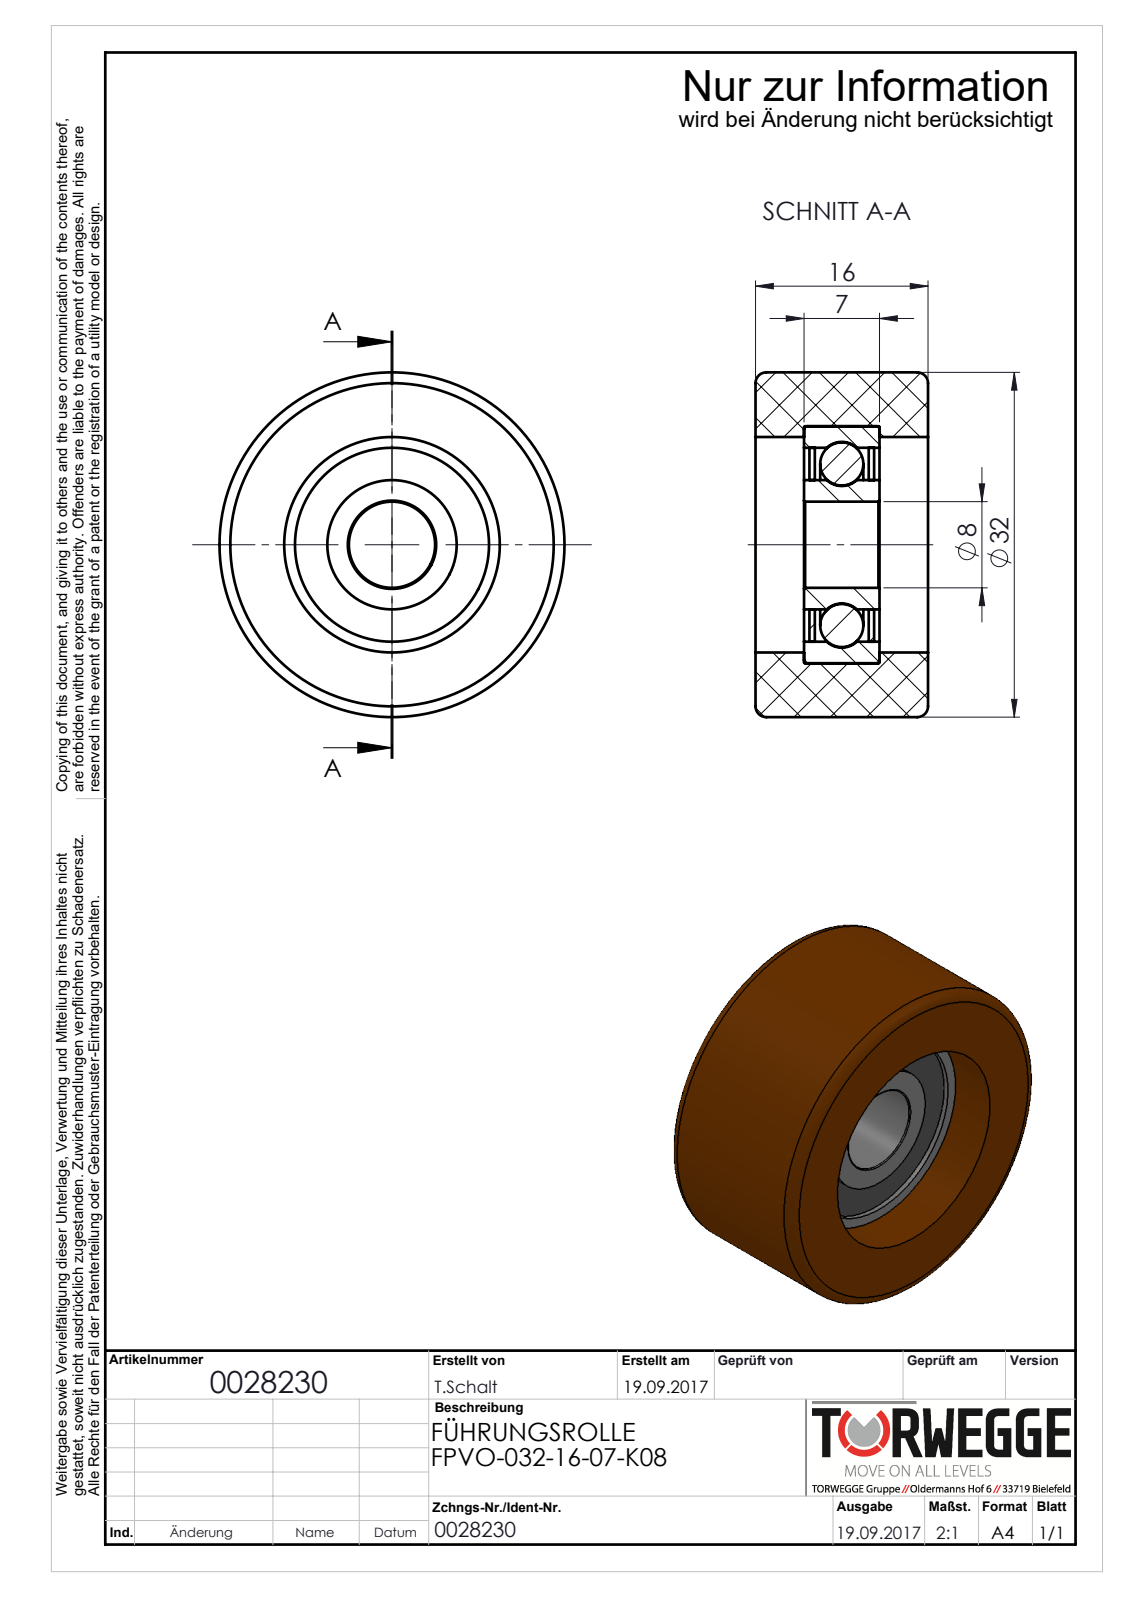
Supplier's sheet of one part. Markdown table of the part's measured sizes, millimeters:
| quantity | value |
| --- | --- |
| part name | FPVO-032-16-07-K08_Bandage; 0028230_FPVO-032-16-07-K08; DIN625_TF_DIN625-608 |
| STEP written by | SolidWorks 2016 (AUTOMOTIVE_DESIGN) |
| units | millimeters |
| bodies | 6 solids, 66 faces (12 planar, 28 cylindrical, 26 other) |
| overall size | 32 × 32 × 16 |
| volume | 9 293 mm³ |
| surface area | 6 632 mm² |
| round holes (diameter × count) | 8 × 1, 12 × 1, 18 × 1, 20 × 1, 22 × 1 |
| round bosses / shafts (diameter × count) | 32 × 1 |
| main face-to-face distances | 0.5, 5.5, 4.5, 11.5, 6, 5, 16, 10.5, 11, 1 |
